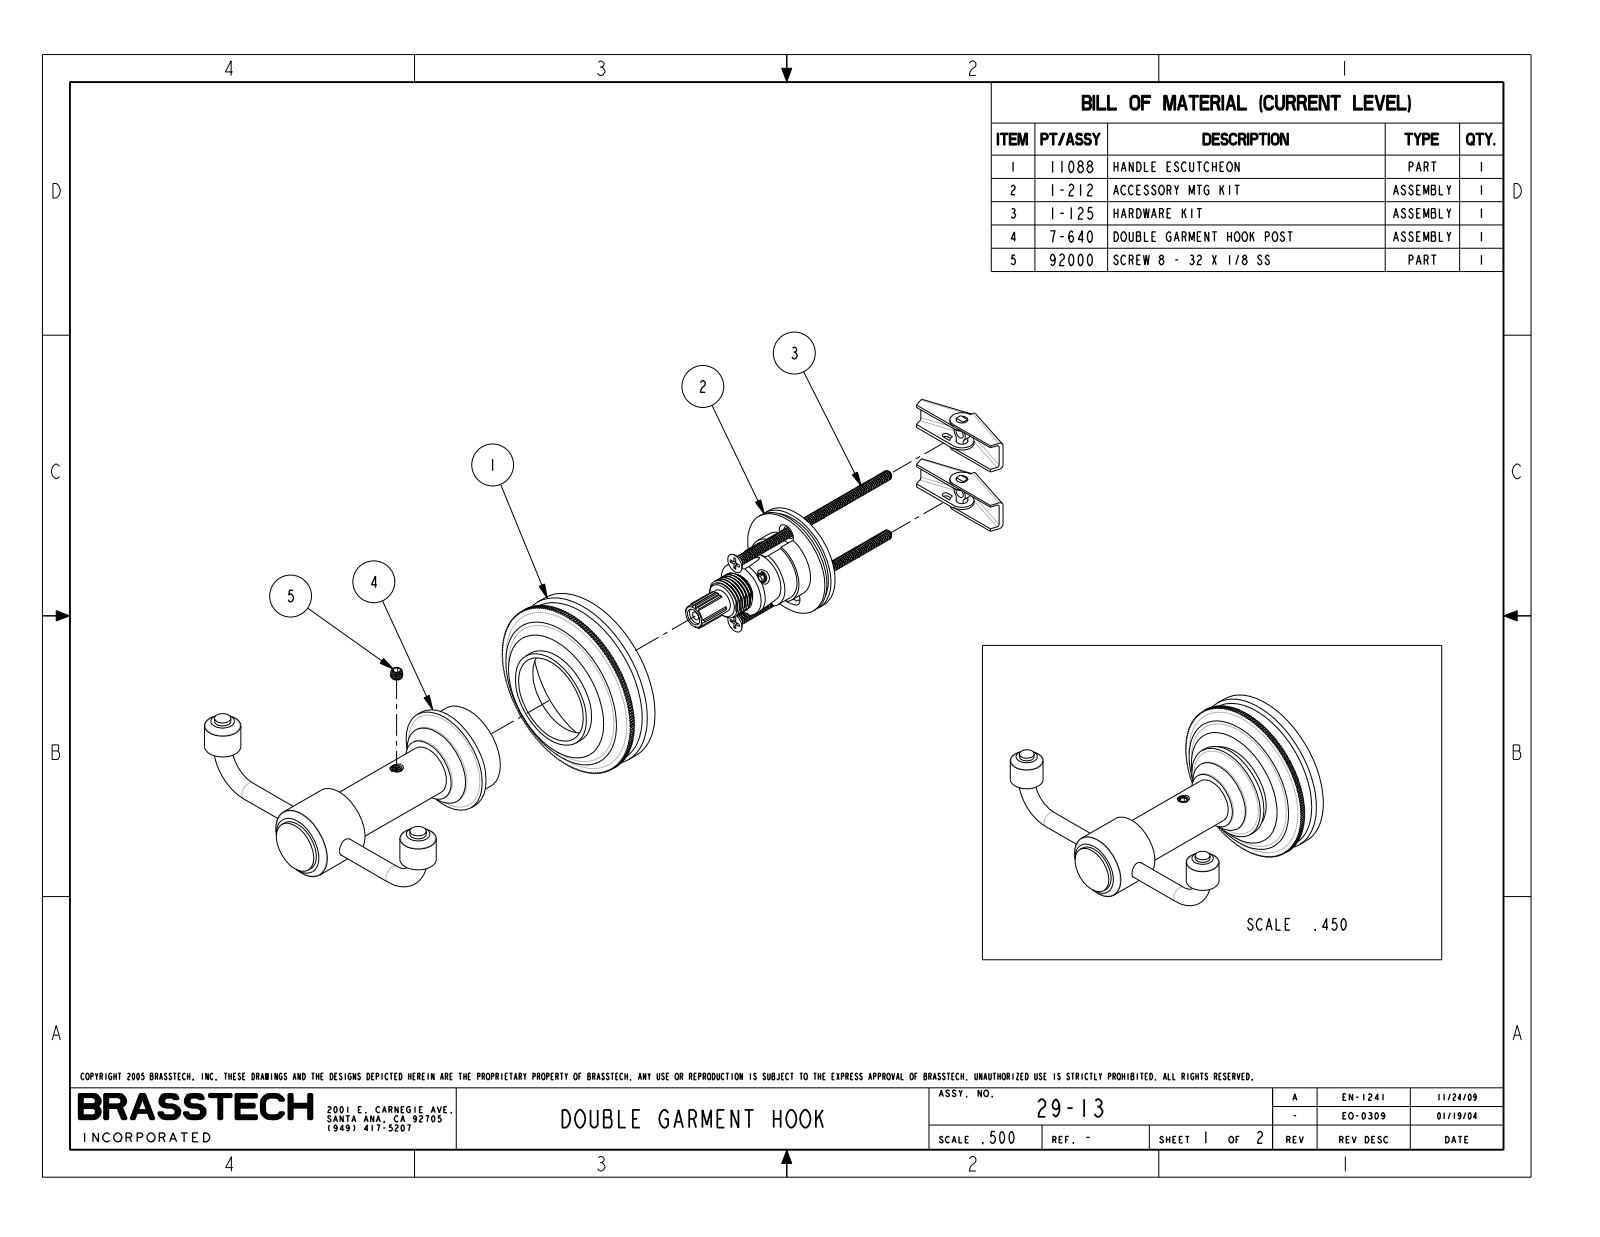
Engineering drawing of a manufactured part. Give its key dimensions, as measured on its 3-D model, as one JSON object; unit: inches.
{"part_name": "29-13_SPEC_SW0001", "step_written_by": "PRO/ENGINEER BY PARAMETRIC TECHNOLOGY CORPORATION, 2009300 (CONFIG_CONTROL_DESIGN)", "units": "inches", "bodies": {"solids": 0, "faces": 612, "planar": 380, "cylindrical": 210, "other": 22}, "overall_size": [4.3, 3.75, 2.5], "round_bosses_or_shafts": [[0.5, 2], [0.225, 2], [2.5, 1], [2.4, 1], [1.48, 1], [1.38, 1], [1.134, 1], [1, 1]], "face_to_face_distances": [0.1, 0.475, 0.4, 0.075, 0.2, 0.575, 0.175, 0.675, 0.275, 0.075]}
